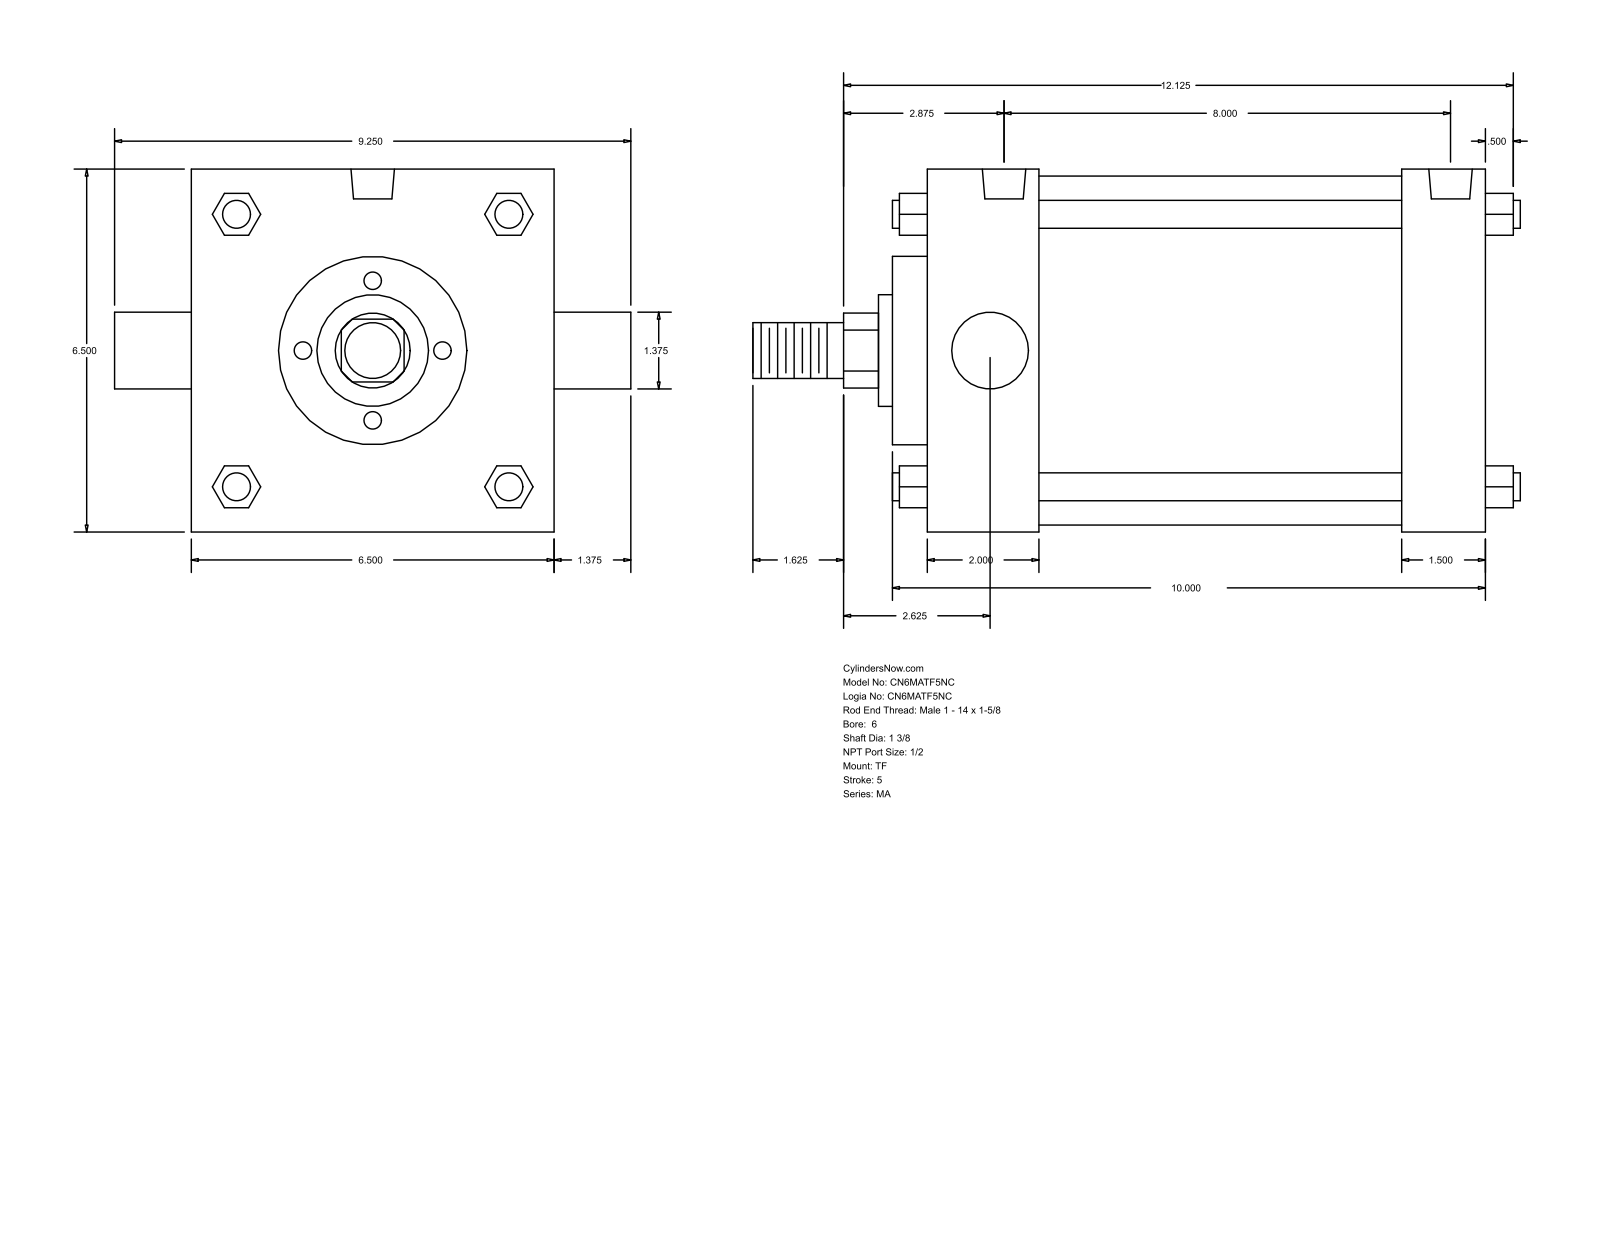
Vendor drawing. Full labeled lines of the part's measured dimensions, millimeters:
Part name (STEP PRODUCT): MA_TF__0600_1.375
STEP written by: GSSL Pune (CONFIG_CONTROL_DESIGN)
Units: millimetres
Bodies: 0 solids, 122 faces (93 planar, 29 cylindrical, 0 other)
Overall size (bounding box): 349.25 × 234.95 × 165.1
Round holes (diameter × count): ⌀17.46 ×3, ⌀19.77 ×2
Round bosses / shafts (diameter × count): ⌀12.7 ×4, ⌀34.92 ×2, ⌀158.75 ×1, ⌀85.72 ×1, ⌀50.8 ×1, ⌀25.4 ×1
Partial cylindrical surfaces — rounded edges, fillets, slot ends (radius × count): R17.06 ×1
Main face-to-face distances: 165.1, 257.17, 50.8, 219.08, 206.37, 168.28, 38.09, 66.67, 15.87, 234.95
Hole centre spacings: 3.18, 203.2, 206.38
